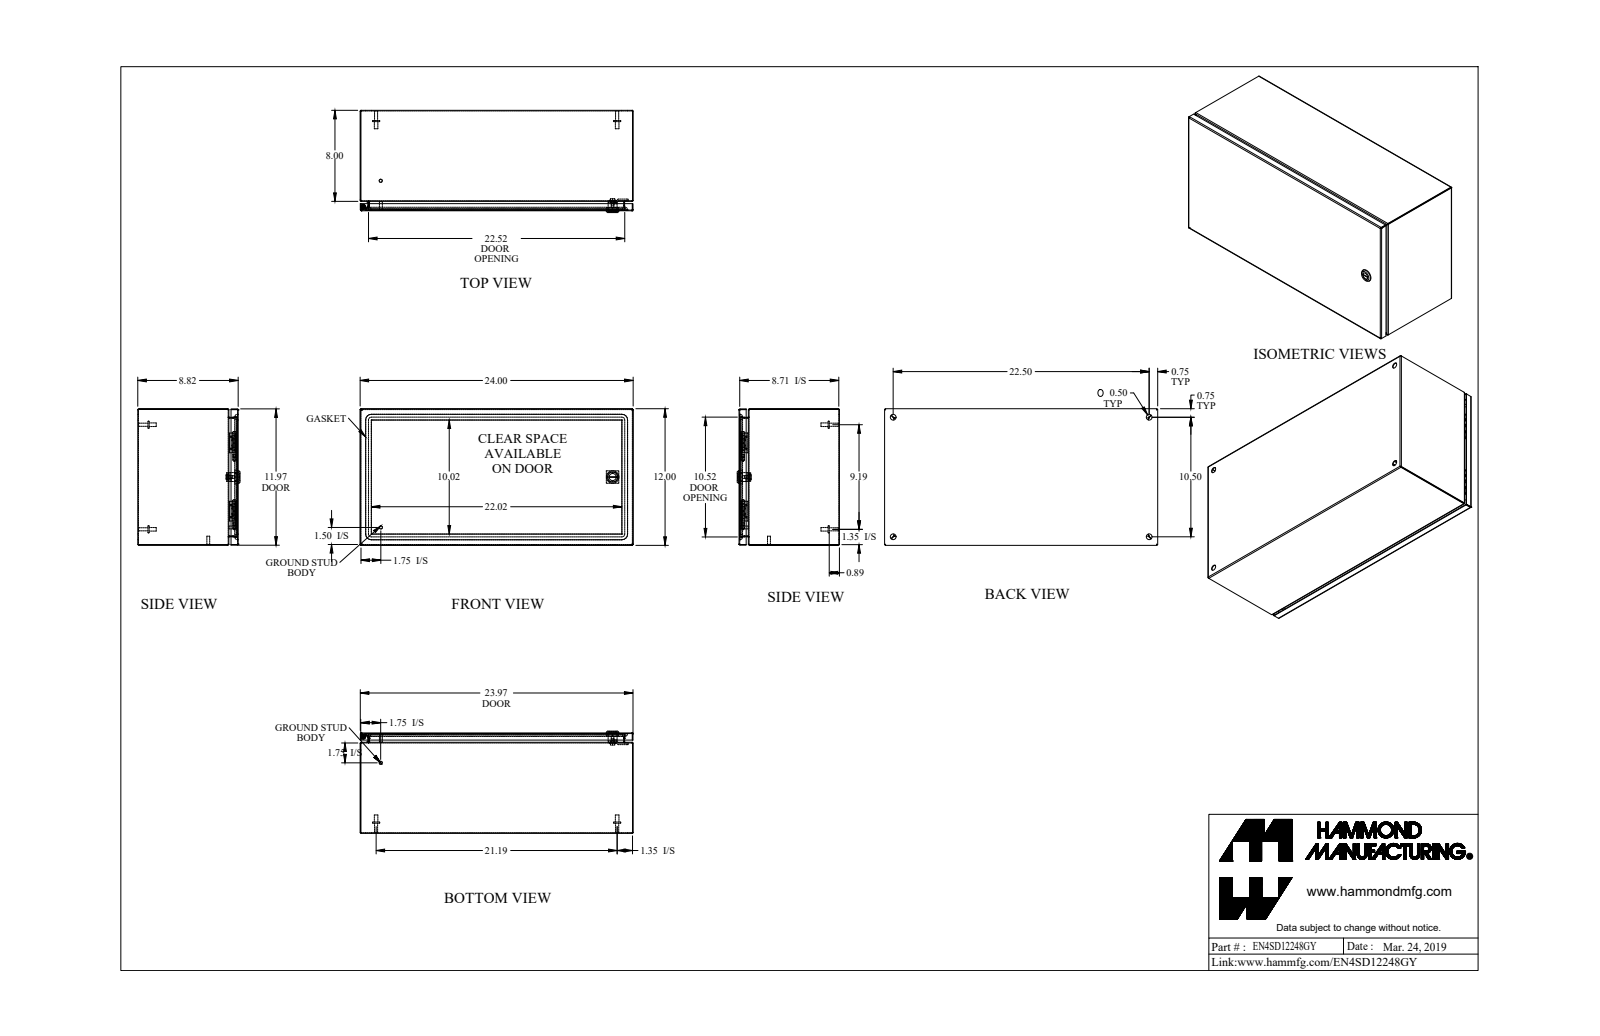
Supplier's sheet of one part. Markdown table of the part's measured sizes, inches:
| quantity | value |
| --- | --- |
| part name | EN4SD12248GY_Default |
| STEP written by | SolidWorks 2019 (CONFIG_CONTROL_DESIGN) |
| units | inches |
| bodies | 21 solids, 634 faces (285 planar, 213 cylindrical, 136 other) |
| overall size | 24 × 12 × 8.982 |
| volume | 80.8 in³ |
| surface area | 2 744 in² |
| round holes (diameter × count) | 0.5 × 4, 0.172 × 1, 0.232 × 1, 0.24 × 1, 0.242 × 1, 0.625 × 1, 0.785 × 1 |
| round bosses / shafts (diameter × count) | 0.625 × 4, 0.313 × 4, 0.27 × 4, 0.281 × 2, 0.25 × 2, 1.1 × 1, 0.525 × 1, 0.455 × 1 |
| partial cylindrical surfaces (radius × count) | 0.029 × 21, 0.086 × 21, 0.25 × 16, 19 × 8, 0.006 × 4, 0.062 × 4, 0.499 × 4, 0.125 × 2 |
| main face-to-face distances | 0.057, 8.765, 11.943, 8.708, 8.822, 11.886, 12, 23.943, 23.886, 24 |
| hole center spacings | 10.5, 22.074, 22.5, 24.83, 5.356, 5.356 |
